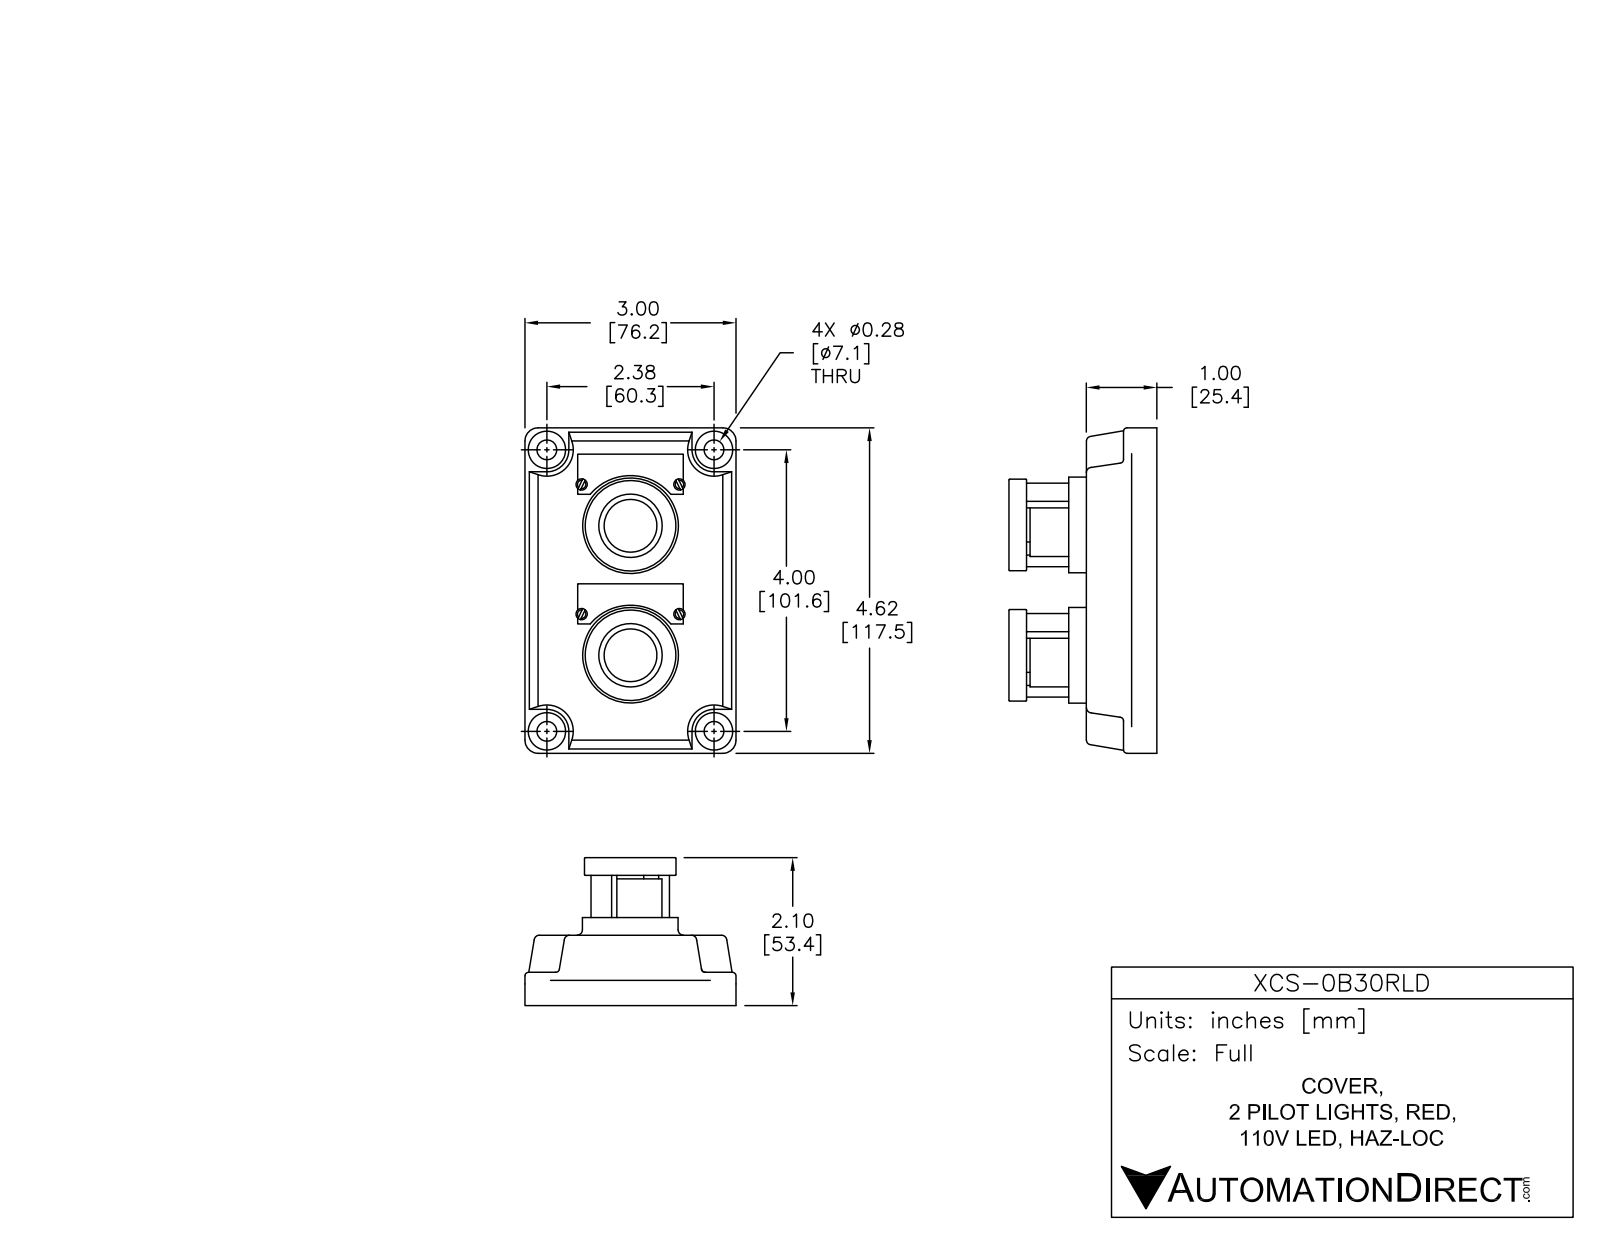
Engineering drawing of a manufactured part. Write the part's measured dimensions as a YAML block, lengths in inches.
part_name: "XCS-0B30RLD"
step_written_by: "SolidWorks 2015 (AUTOMOTIVE_DESIGN)"
units: inches
bodies: {solids: 28, faces: 579, planar: 219, cylindrical: 195, other: 165}
overall_size: [4.625, 3.112, 2.769]
volume: 10.08
surface_area: 103.8
round_holes:
  - {diameter: 0.285, count: 4}
  - {diameter: 0.248, count: 2}
  - {diameter: 0.689, count: 2}
  - {diameter: 0.89, count: 2}
  - {diameter: 1.26, count: 2}
round_bosses_or_shafts:
  - {diameter: 0.16, count: 8}
  - {diameter: 0.457, count: 4}
  - {diameter: 0.25, count: 4}
  - {diameter: 1.45, count: 2}
  - {diameter: 1.25, count: 2}
  - {diameter: 0.866, count: 2}
  - {diameter: 0.6, count: 2}
  - {diameter: 0.394, count: 2}
partial_cylinders:
  - {radius: 0.059, count: 16}
  - {radius: 0.079, count: 12}
  - {radius: 0.03, count: 8}
  - {radius: 0.118, count: 8}
  - {radius: 0.25, count: 8}
  - {radius: 0.055, count: 6}
  - {radius: 0.06, count: 6}
  - {radius: 0.02, count: 4}
face_to_face_distances: [1.024, 0.059, 0.498, 0.525, 0.458, 0.956, 1.481, 0.399, 0.897, 1.422]
hole_center_spacings: [1.87, 0.018, 1.584, 1.587, 3.159, 3.164, 4, 4.639]
